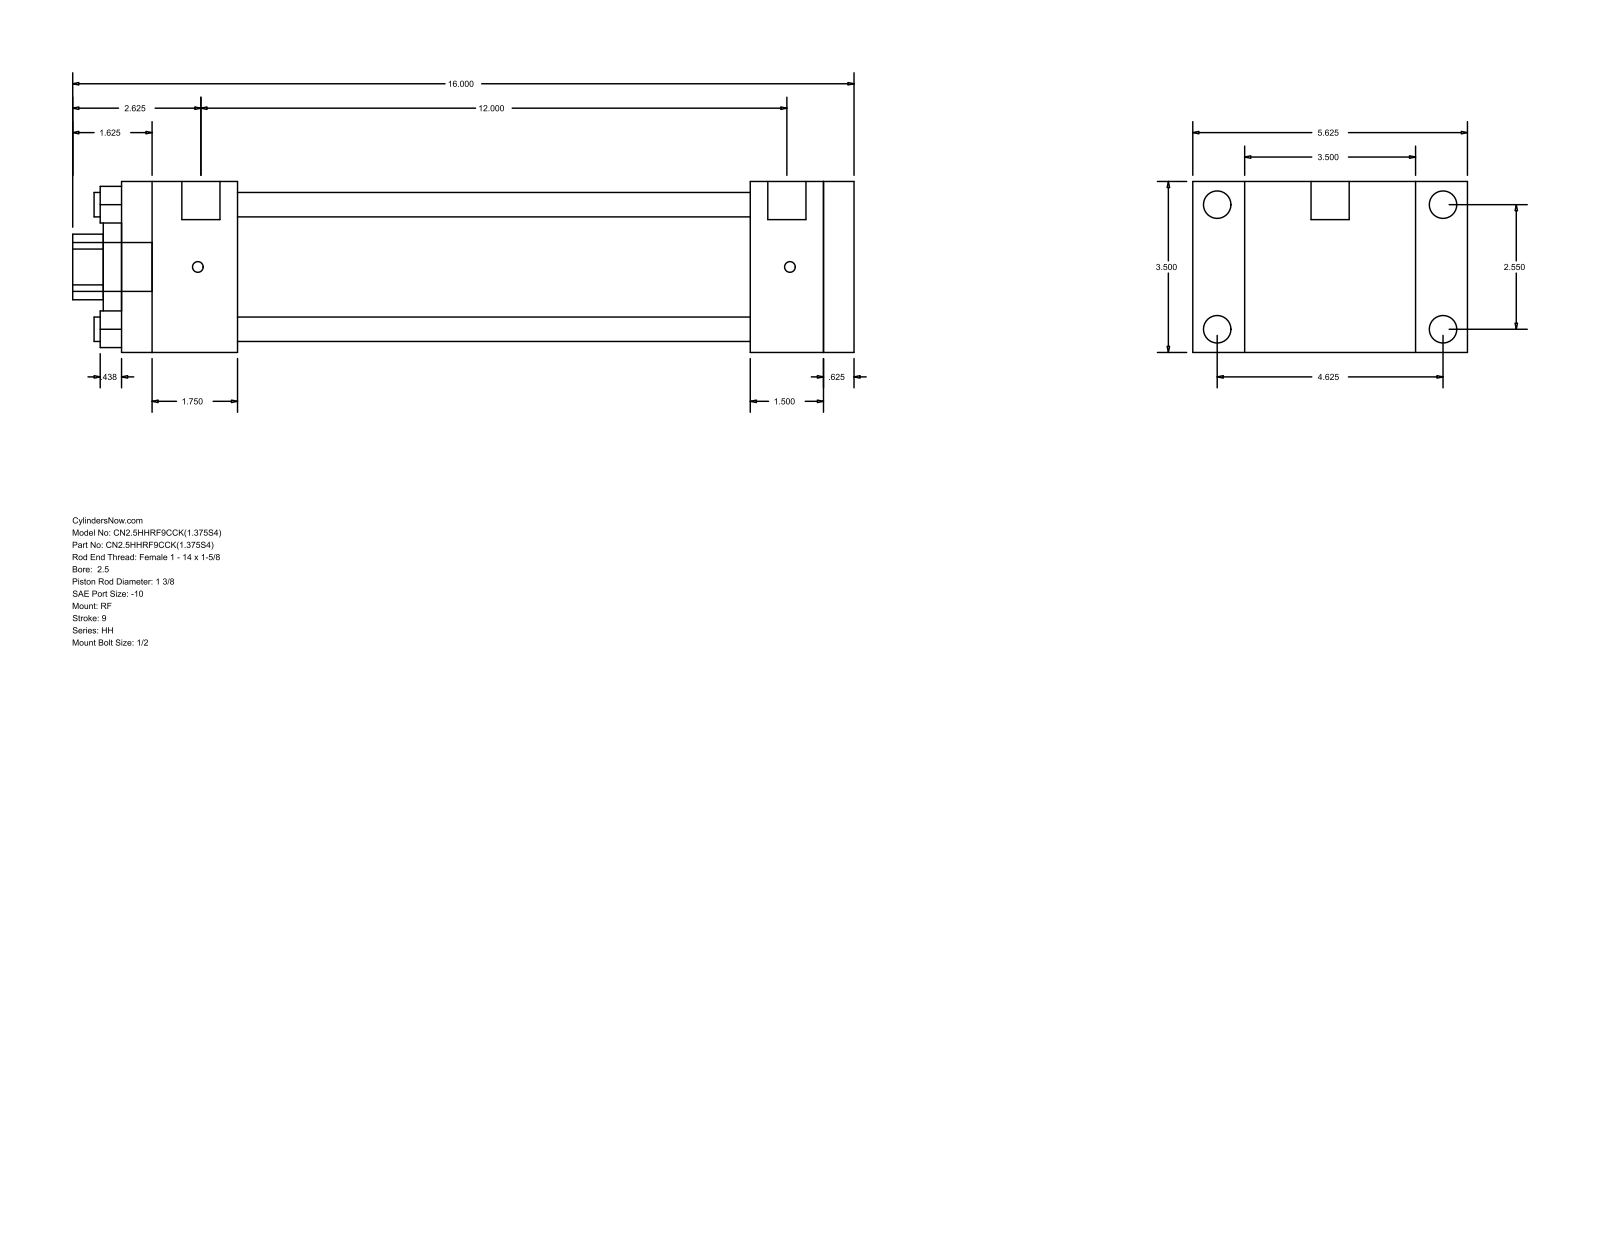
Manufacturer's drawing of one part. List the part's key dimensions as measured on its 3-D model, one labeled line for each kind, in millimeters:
Part name (STEP PRODUCT): HH_RF__0250_1.375
STEP written by: GSSL Pune (CONFIG_CONTROL_DESIGN)
Units: millimetres
Bodies: 0 solids, 92 faces (64 planar, 28 cylindrical, 0 other)
Overall size (bounding box): 406.4 × 142.88 × 88.9
Round holes (diameter × count): ⌀12.7 ×4, ⌀34.92 ×1, ⌀50.8 ×1, ⌀73.03 ×1
Round bosses / shafts (diameter × count): ⌀14.3 ×4, ⌀5.56 ×4, ⌀19.84 ×2, ⌀25.4 ×1
Partial cylindrical surfaces — rounded edges, fillets, slot ends (radius × count): R17.06 ×1
Main face-to-face distances: 88.9, 381, 15.88, 365.12, 60.32, 304.8, 320.68, 327.03, 266.71, 38.09
Hole centre spacings: 45.79, 64.76, 91.58
